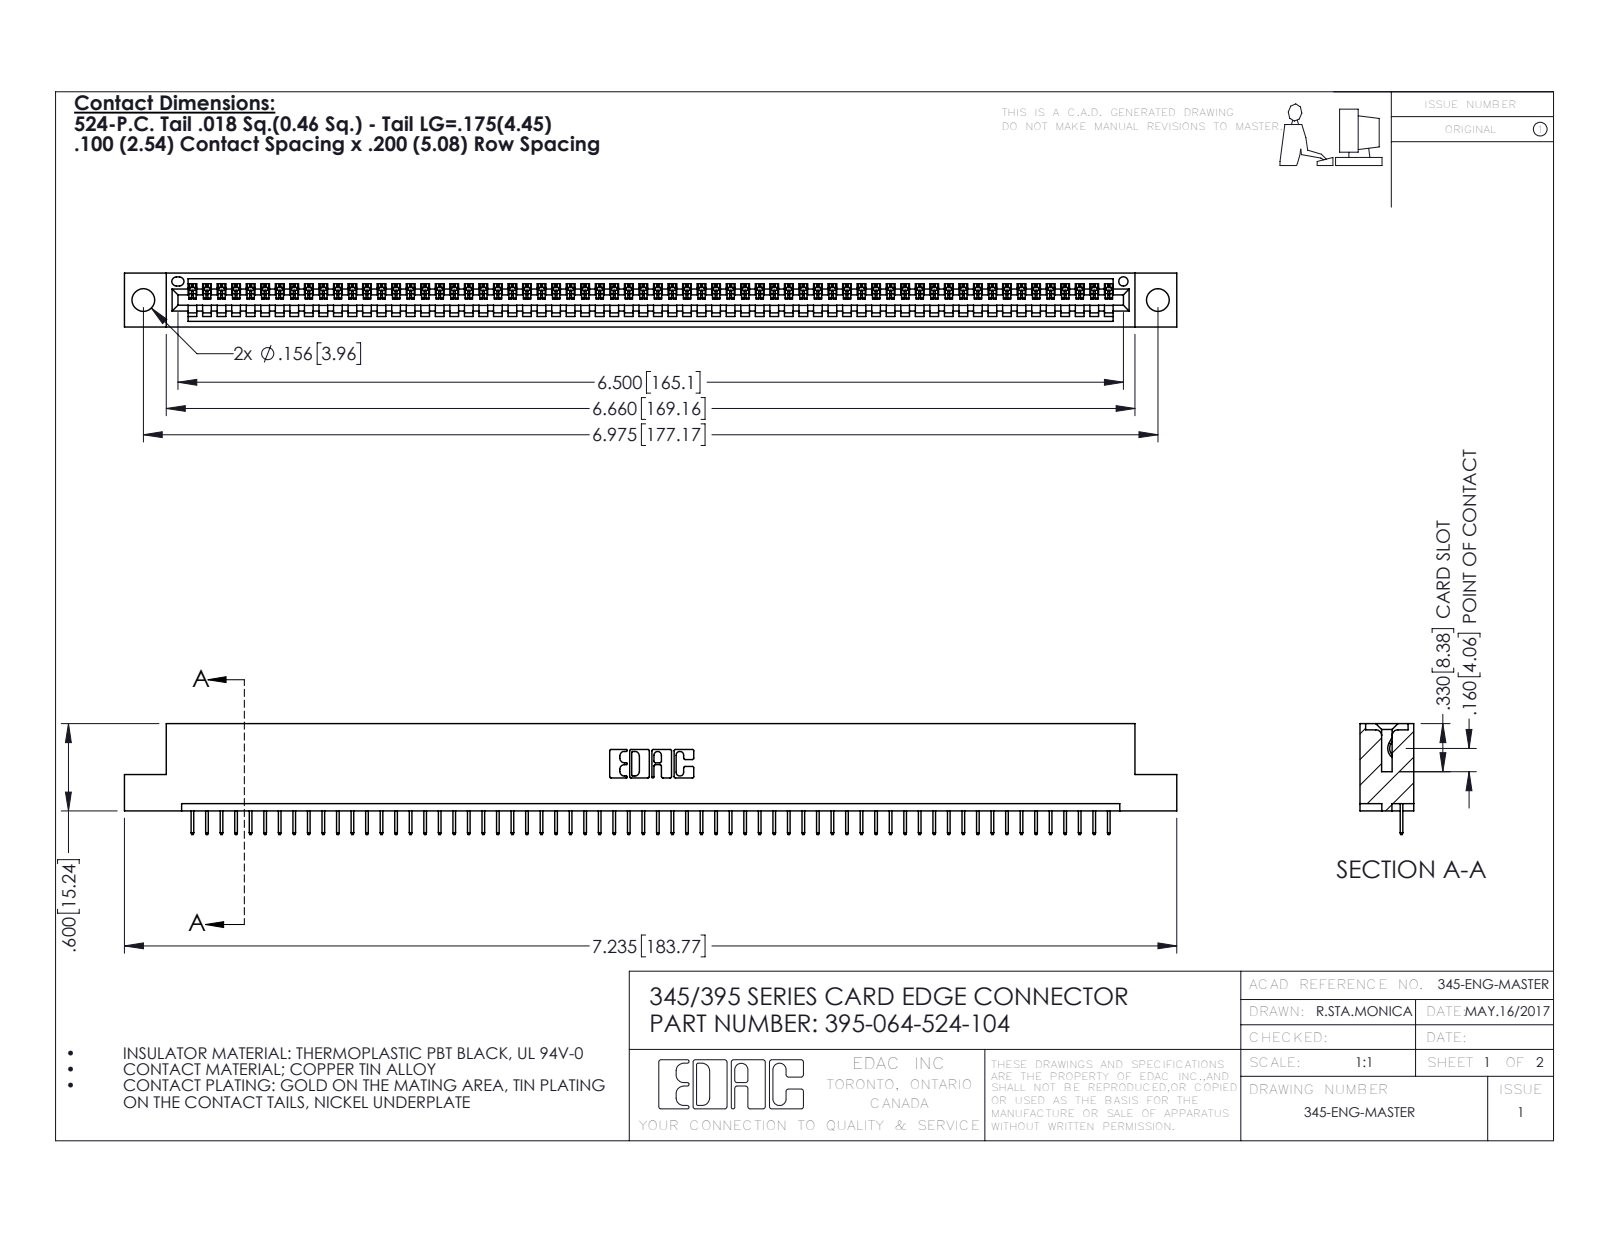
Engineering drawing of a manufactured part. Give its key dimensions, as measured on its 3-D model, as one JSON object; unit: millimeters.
{"part_name": "345-292-001_345-293-124; 395-064-524-104; 345 Part_Flush Mounting Lugs - 0.156 Dia-TH", "step_written_by": "SolidWorks 2016 (CONFIG_CONTROL_DESIGN)", "units": "millimeters", "bodies": {"solids": 65, "faces": 4094, "planar": 3024, "cylindrical": 1070, "other": 0}, "overall_size": [183.8, 19.4, 9.4], "volume_mm3": 17290, "surface_area_mm2": 22280, "round_holes": [[4, 2], [1.6, 1]], "partial_cylinders_radius": [[0.2, 128], [0.3, 22], [0.2, 6], [0.8, 6], [0.7, 3], [0.8, 2], [1, 2], [0.4, 1]], "face_to_face_distances": [7.6, 1.8, 9.4, 5.1, 2.5, 6.9, 0.6, 5.7, 1.8, 3.8], "hole_center_spacings": [6.9, 171.2, 177.2]}
